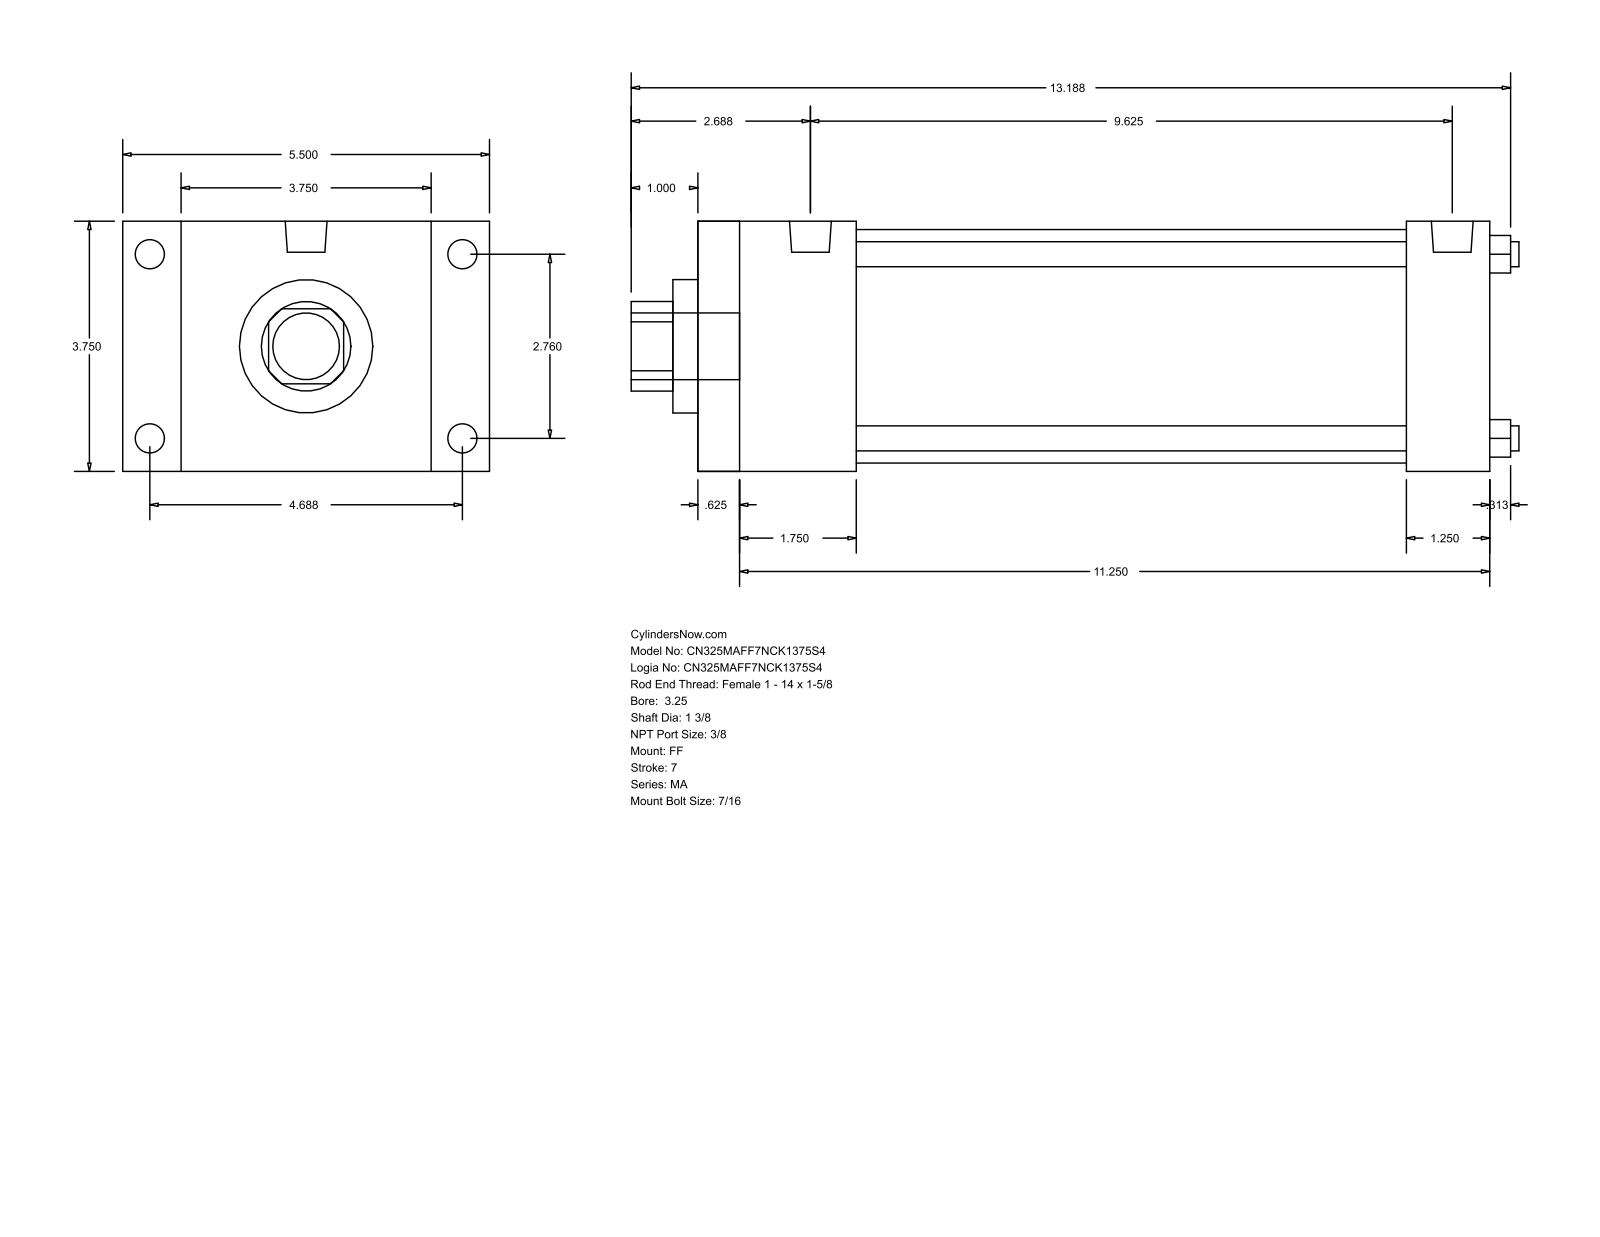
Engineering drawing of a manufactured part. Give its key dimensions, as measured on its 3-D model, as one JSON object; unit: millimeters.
{"part_name": "MA_FF__0325_1.375", "step_written_by": "GSSL Pune (CONFIG_CONTROL_DESIGN)", "units": "millimeters", "bodies": {"solids": 0, "faces": 92, "planar": 64, "cylindrical": 28, "other": 0}, "overall_size": [338.14, 139.7, 95.25], "round_holes": [[9.53, 4], [34.92, 1], [50.8, 1], [88.9, 1]], "round_bosses_or_shafts": [[11.11, 8], [15.93, 2], [25.4, 1]], "partial_cylinders_radius": [[17.06, 1]], "face_to_face_distances": [95.24, 301.62, 15.87, 285.75, 22.23, 117.47, 60.32, 269.87, 44.45, 254], "hole_center_spacings": [49.57, 70.1, 99.14]}
